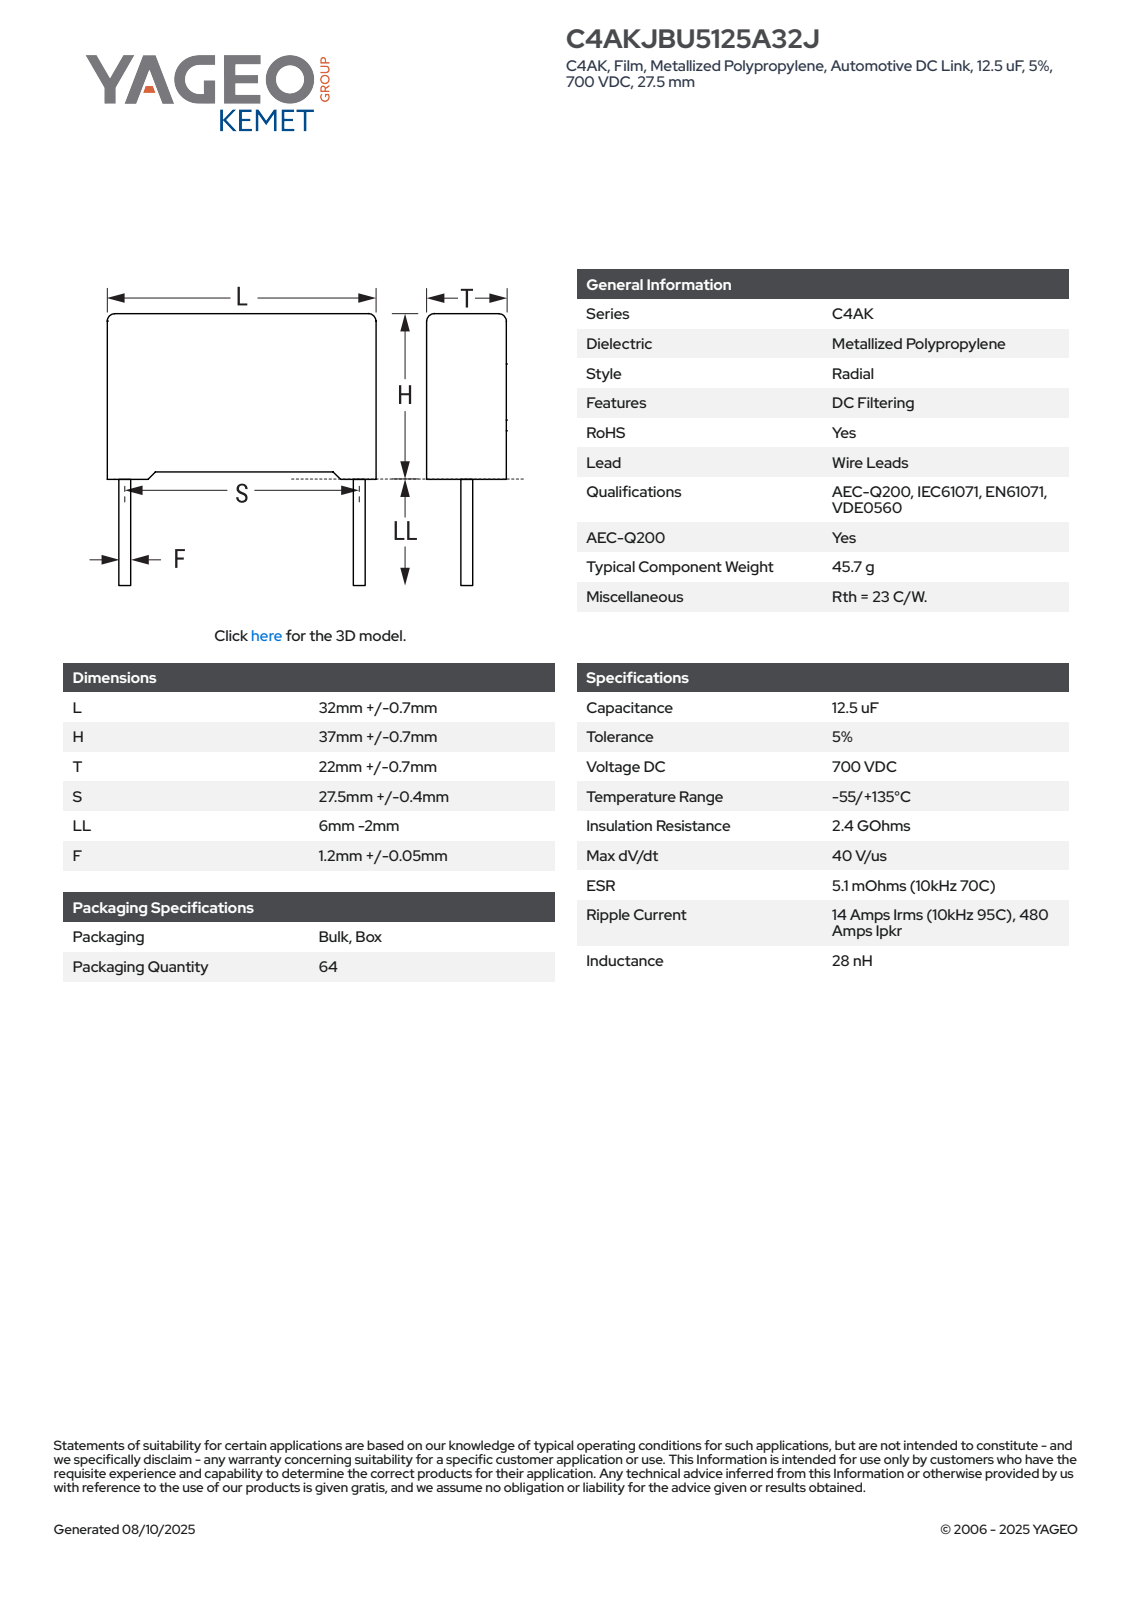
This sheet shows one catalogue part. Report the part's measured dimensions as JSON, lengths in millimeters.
{"part_name": "CFR_RB2CFP_32X37X22_L32.7H37.7T22.7S27.5LL4F1.25", "step_written_by": "SolidWorks 2014 (AUTOMOTIVE_DESIGN)", "units": "millimeters", "bodies": {"solids": 4, "faces": 85, "planar": 77, "cylindrical": 8, "other": 0}, "overall_size": [41.7, 32.7, 22.7], "volume_mm3": 27193, "surface_area_mm2": 5749, "round_bosses_or_shafts": [[1.25, 2]], "partial_cylinders_radius": [[0.5, 4]], "face_to_face_distances": [22.7, 32.7, 36.4, 0.55, 36.95, 0.75, 1.3, 37.7, 1.09, 31.61]}
